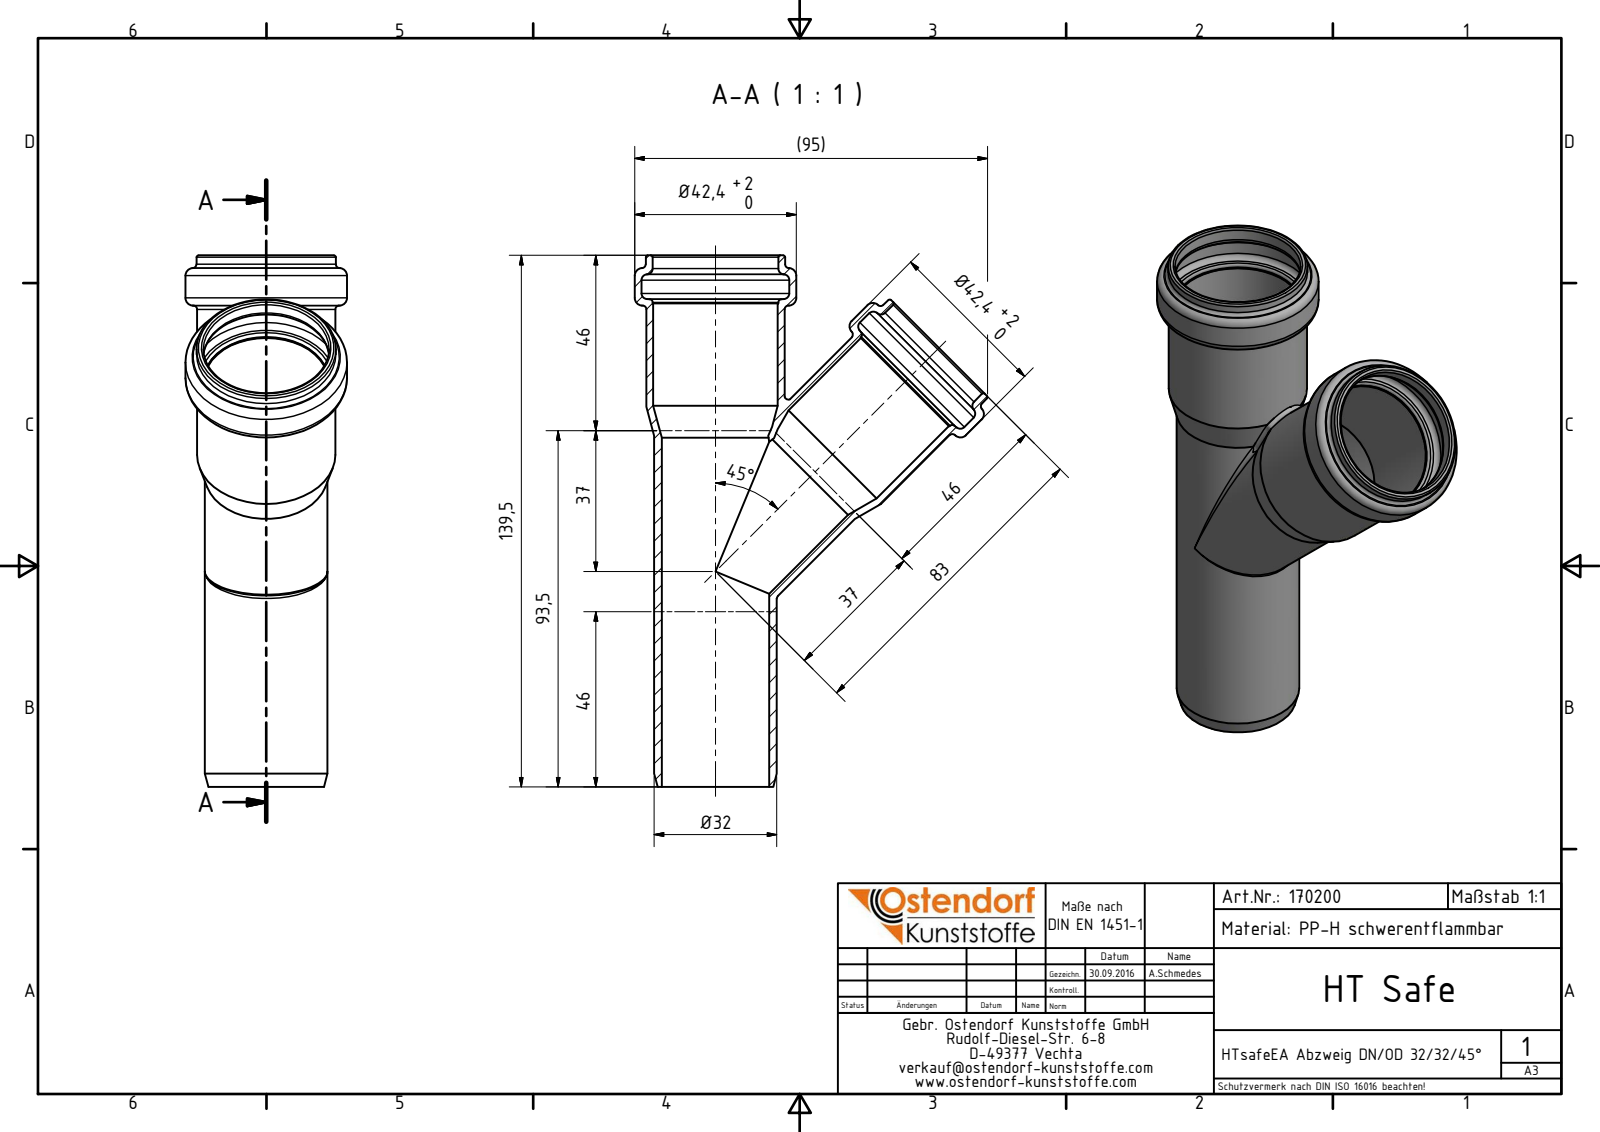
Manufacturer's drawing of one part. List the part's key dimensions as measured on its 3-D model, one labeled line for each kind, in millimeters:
Part name (STEP PRODUCT): 170200 HTsafeEA DN_OD 32_32_45°
STEP written by: Autodesk Inventor 2016 (AUTOMOTIVE_DESIGN)
Units: millimetres
Bodies: 1 solid, 64 faces (9 planar, 18 cylindrical, 37 other)
Overall size (bounding box): 139.5 × 92.62 × 42.4
Volume: 39 903 mm³ · Surface area: 41 982 mm²
Round holes (diameter × count): ⌀28.2 ×2, ⌀32.7 ×2, ⌀33 ×2, ⌀38.8 ×2
Round bosses / shafts (diameter × count): ⌀42.4 ×2, ⌀36.6 ×2, ⌀36.3 ×2, ⌀32.2 ×2
Main face-to-face distances: 139.5, 12.63, 126.88, 12.62, 1.6
